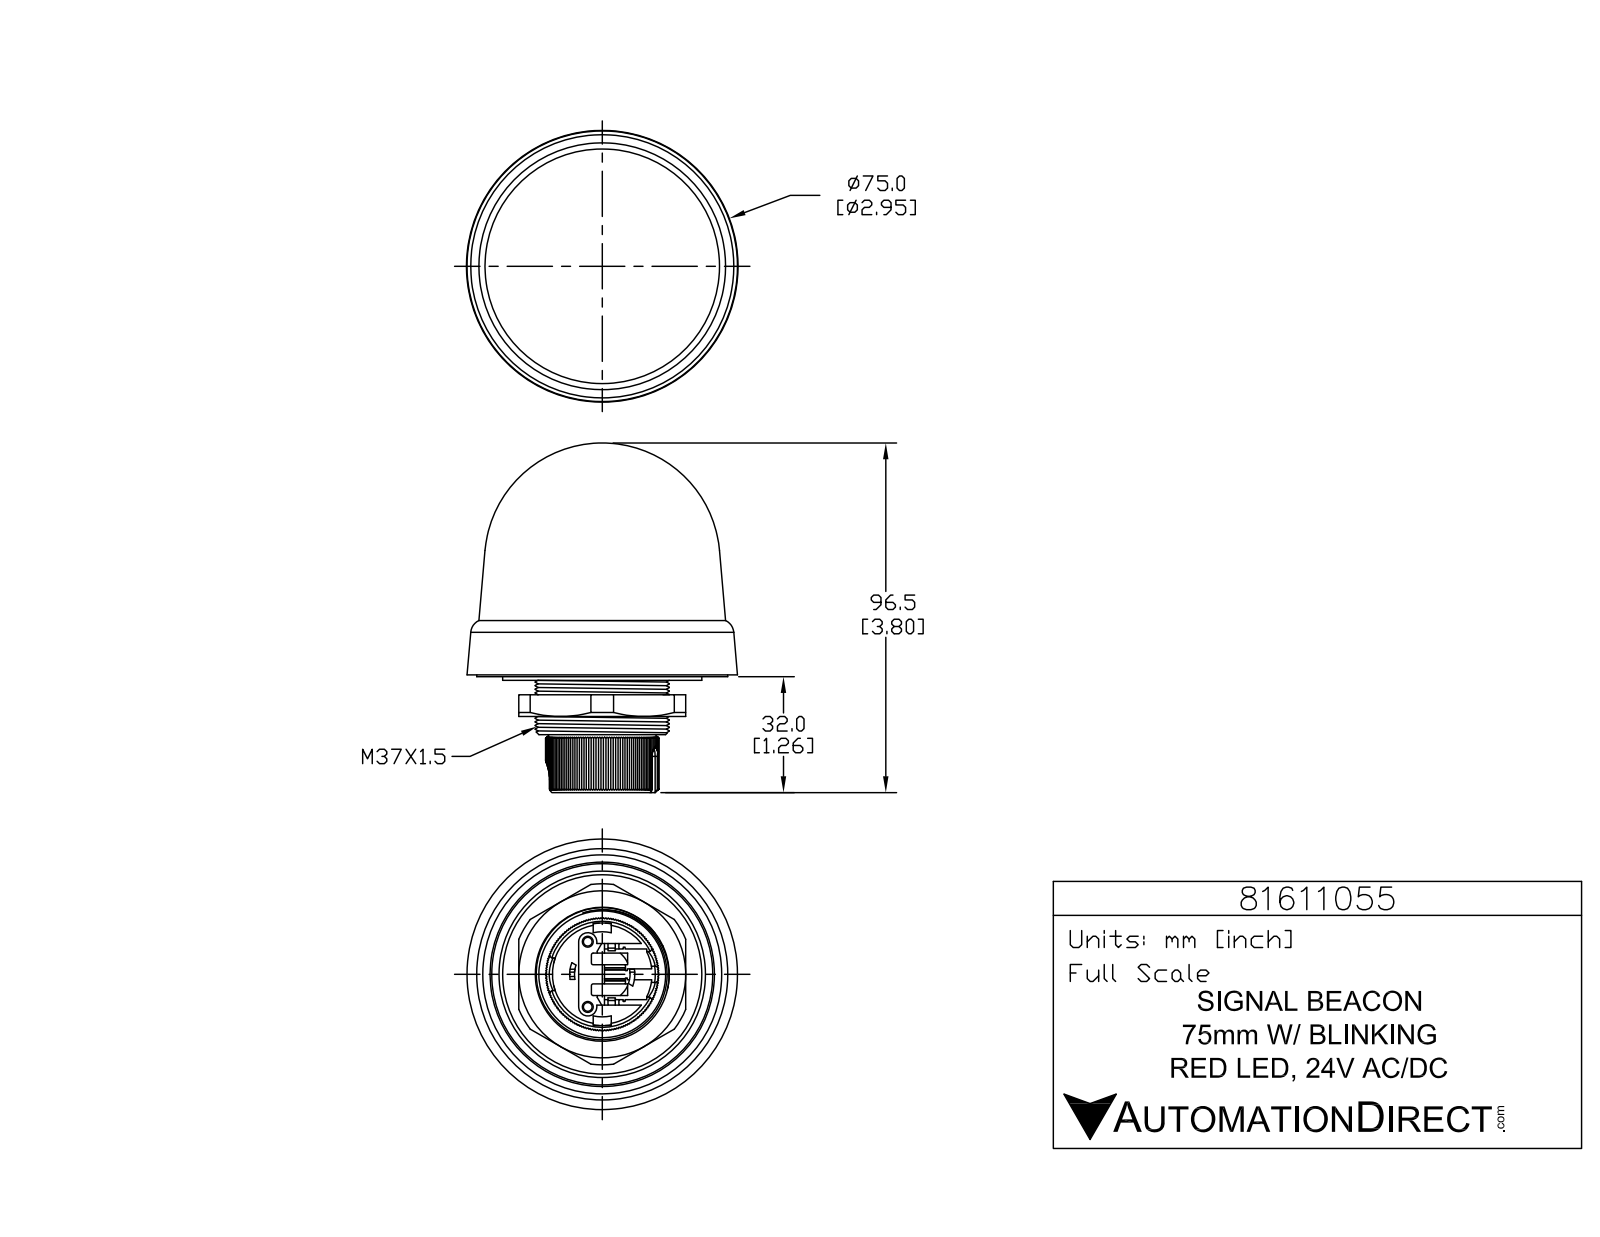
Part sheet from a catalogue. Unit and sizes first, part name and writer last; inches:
Units: inches
Overall size (bounding box): 3.799 × 2.941 × 2.941
Round holes (diameter × count): ⌀0.094 ×2, ⌀0.118 ×2, ⌀0.604 ×1, ⌀1.142 ×1
Round bosses / shafts (diameter × count): ⌀0.217 ×2, ⌀0.067 ×2, ⌀2.165 ×1, ⌀1.457 ×1, ⌀0.925 ×1
Partial cylindrical surfaces — rounded edges, fillets, slot ends (radius × count): R0.008 ×6, R0.039 ×6, R0.02 ×4, R0.031 ×2, R0.079 ×2, R0.098 ×2, R0.177 ×1, R0.354 ×1
Main face-to-face distances: 0.177, 0.354, 0.197, 0.433, 0.512, 0.335, 0.059, 0.394, 0.118, 0.157
Hole centre spacings: 0.388, 0.709
Volume: 12.36 in³ · Surface area: 58.68 in²
Bodies: 3 solids, 560 faces (432 planar, 80 cylindrical, 48 other)
Part name (STEP PRODUCT): 81611055
STEP written by: SolidWorks 2019 (CONFIG_CONTROL_DESIGN)
